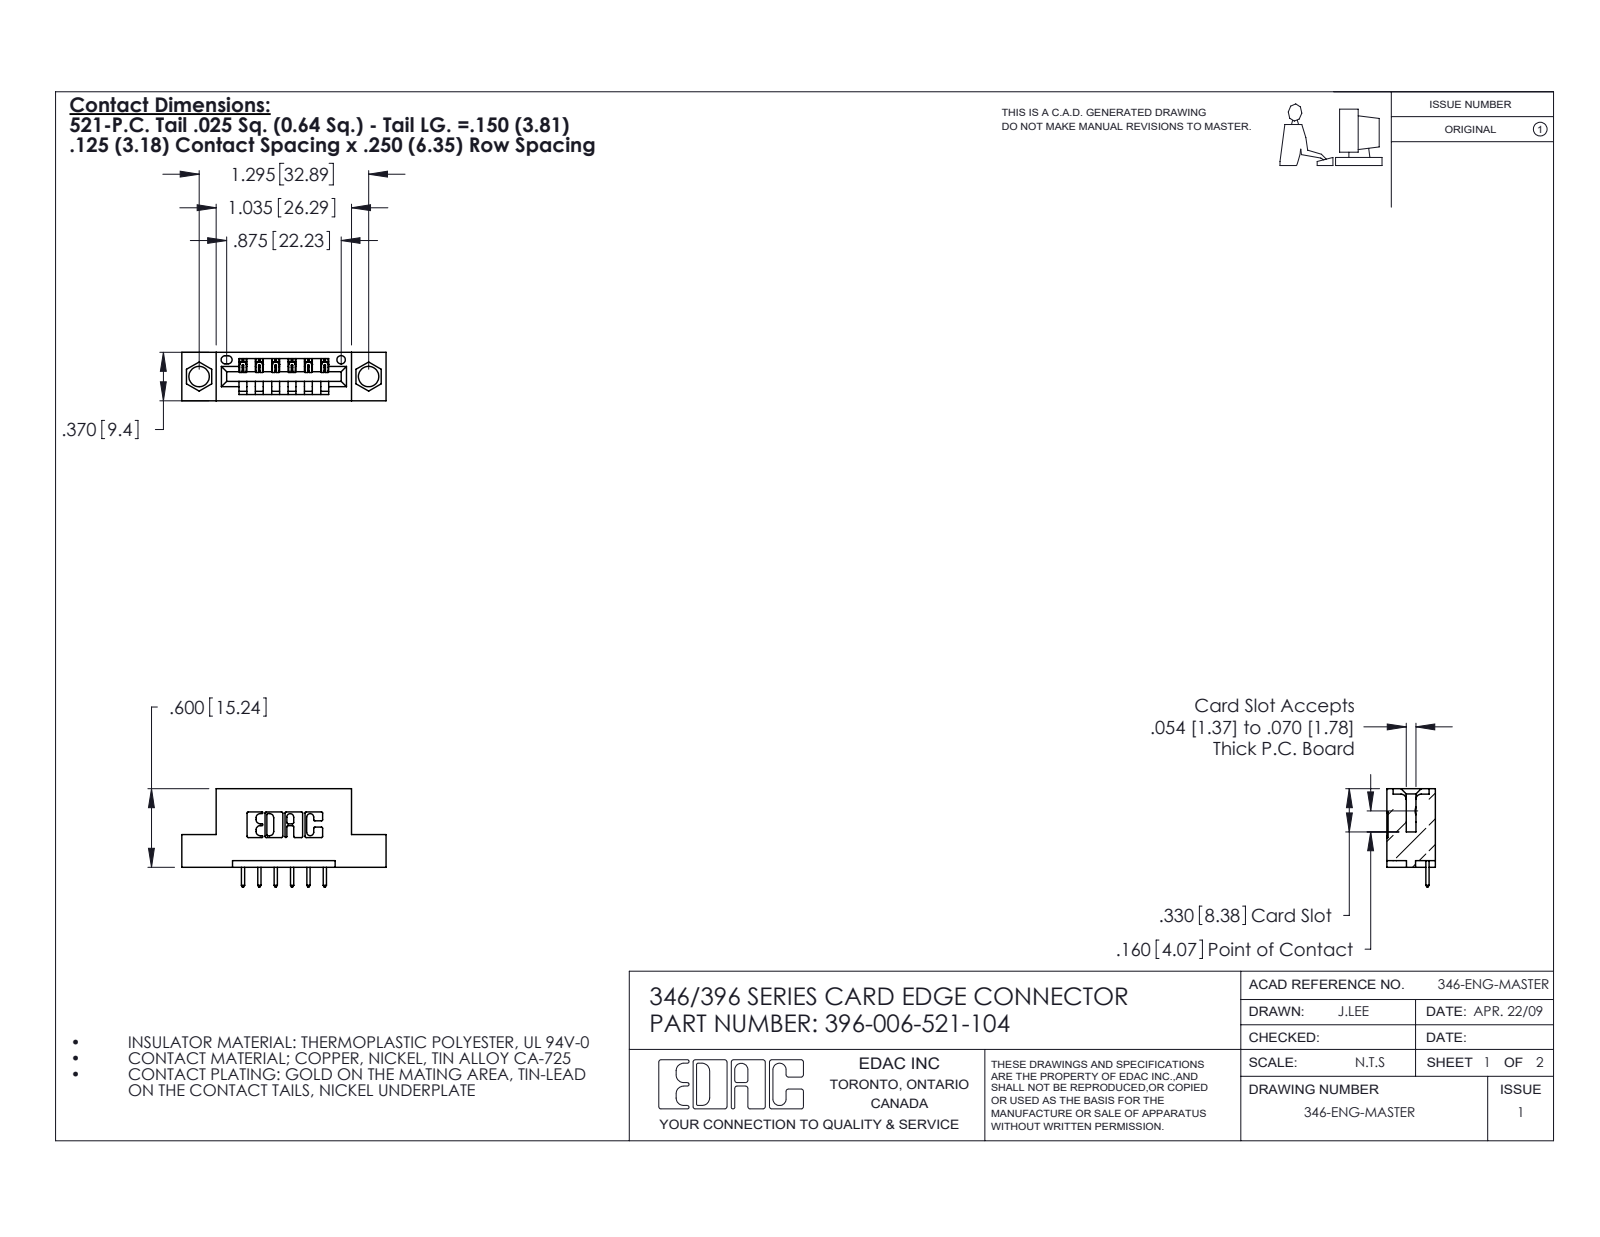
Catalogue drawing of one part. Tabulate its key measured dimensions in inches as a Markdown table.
| quantity | value |
| --- | --- |
| part name | 346 Part_Flush Mounting Lugs - 0.156 Dia-TH; 396-006-521-104; 345-292-001_345-293-121 |
| STEP written by | SolidWorks 2020 (CONFIG_CONTROL_DESIGN) |
| units | inches |
| bodies | 7 solids, 484 faces (330 planar, 154 cylindrical, 0 other) |
| overall size | 1.56 × 0.75 × 0.37 |
| volume | 0.209 in³ |
| surface area | 5.67 in² |
| round holes (diameter × count) | 0.156 × 2, 0.064 × 1 |
| partial cylindrical surfaces (radius × count) | 0.01 × 22, 0.006 × 12, 0.01 × 12, 0.007 × 6, 0.031 × 6, 0.026 × 3, 0.031 × 2, 0.04 × 2 |
| main face-to-face distances | 0.25, 0.37, 0.048, 0.322, 0.148, 0.222, 0.1, 0.174, 0.125, 0.125 |
| hole center spacings | 0.246, 1.092, 1.295 |
